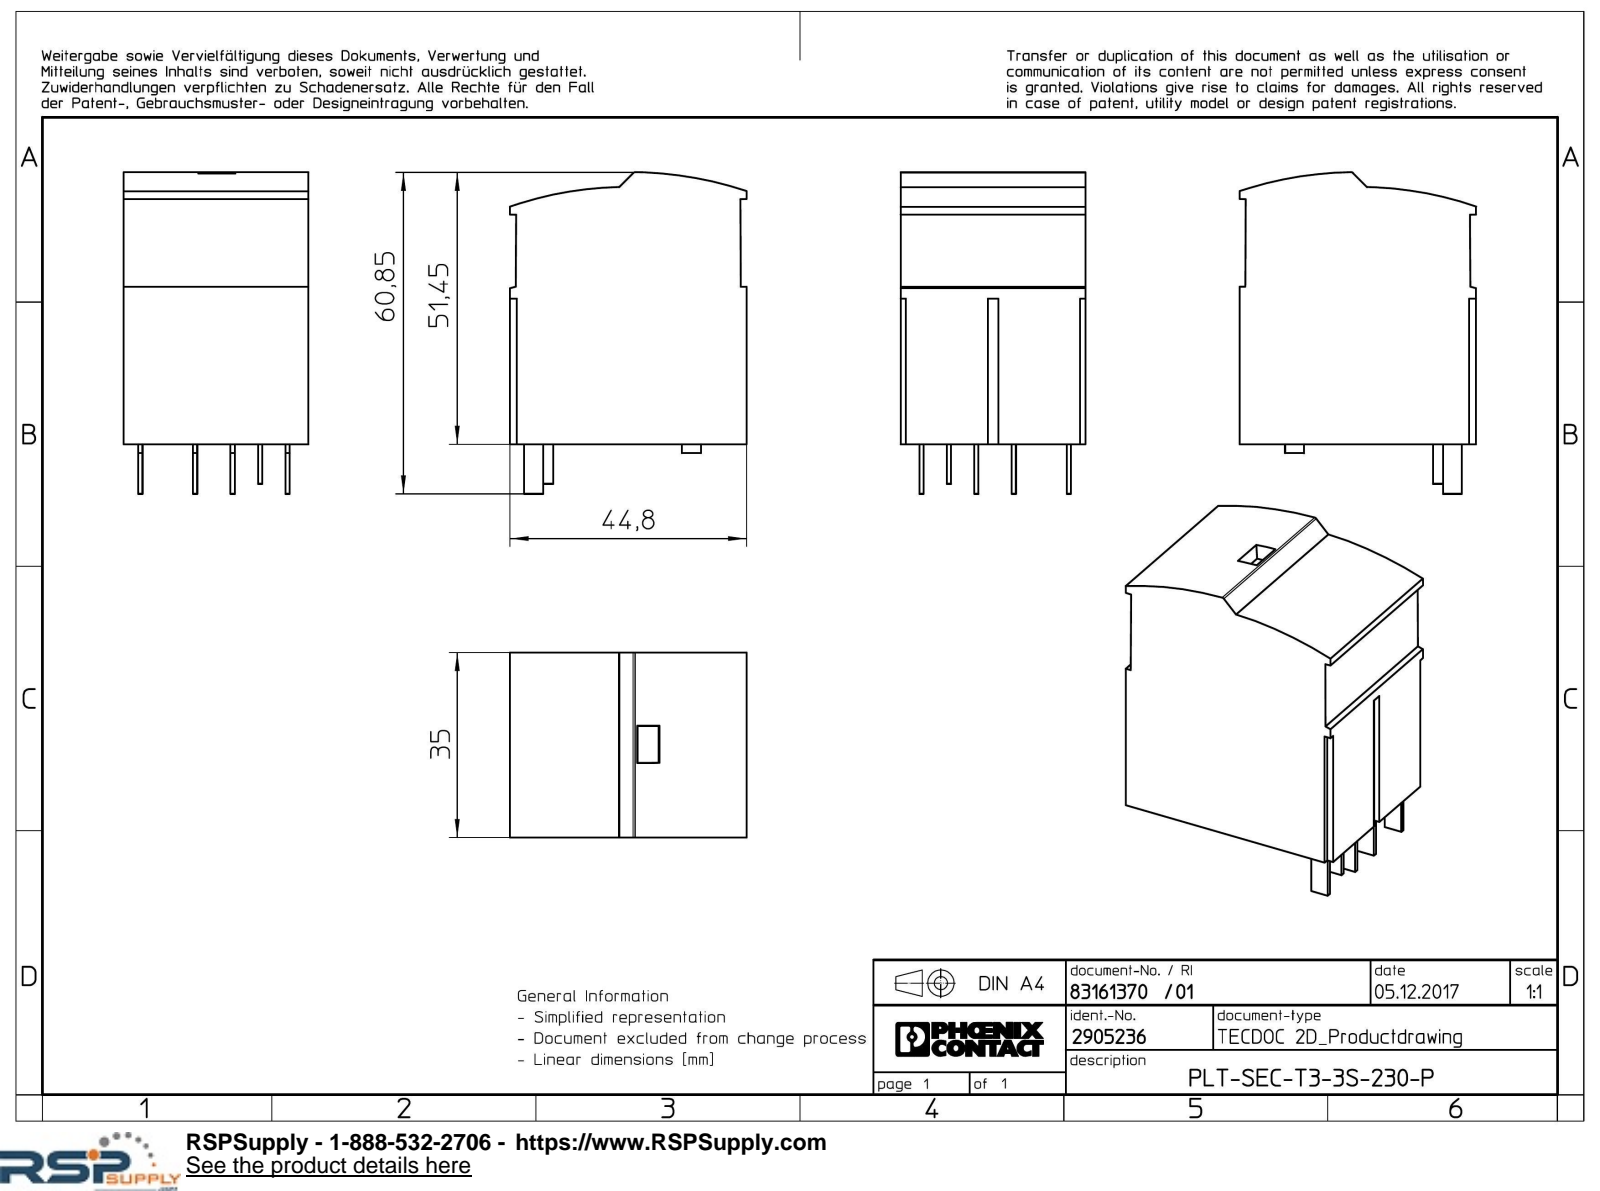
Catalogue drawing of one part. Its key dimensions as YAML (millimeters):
part_name: "PLT_SEC_T3_3S_230_P-select"
step_written_by: "Creo Elements/Direct Modeling 20.1A 29-Sep-2018 (C) Parametric Technology GmbH (AUTOMOTIVE_DESIGN)"
units: millimeters
bodies: {solids: 1, faces: 137, planar: 132, cylindrical: 3, other: 2}
overall_size: [60.85, 44.8, 35]
volume: 70115
surface_area: 13299
partial_cylinders:
  - {radius: 0.5, count: 1}
  - {radius: 69, count: 1}
  - {radius: 71.8, count: 1}
face_to_face_distances: [35, 44.8, 17.5, 0.8, 10.4, 3.75, 5.2, 1, 34, 1.1]
